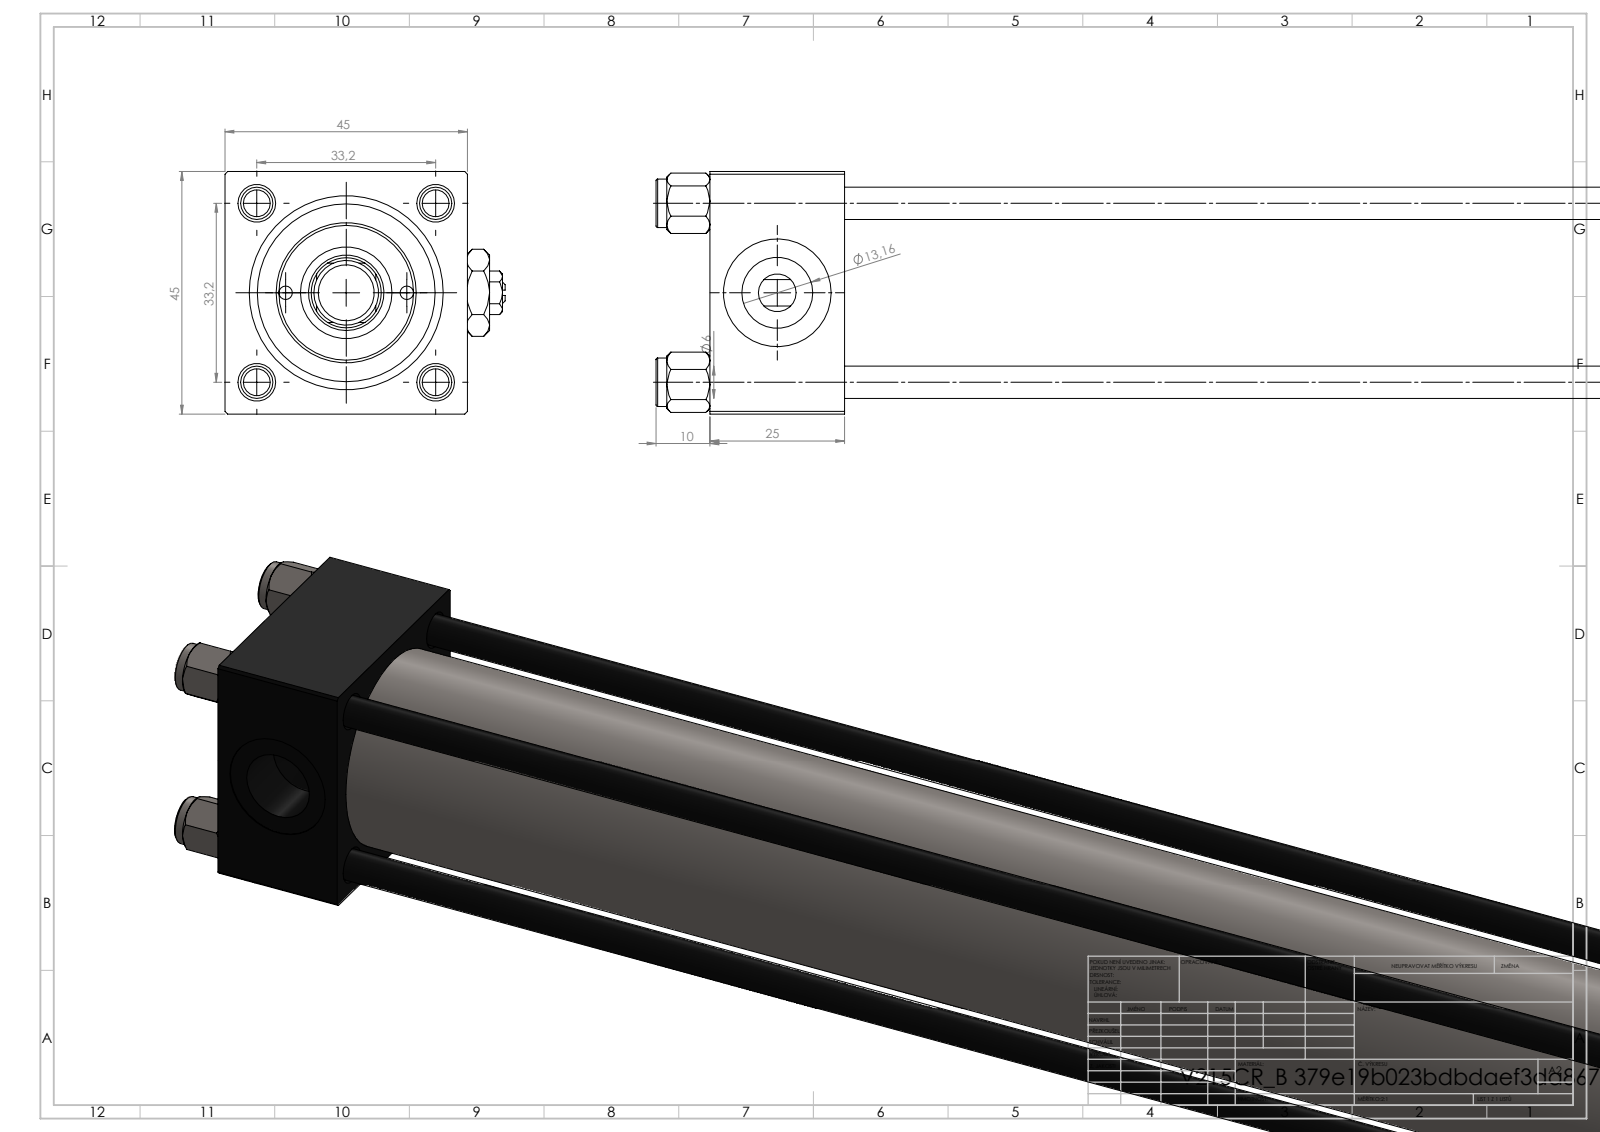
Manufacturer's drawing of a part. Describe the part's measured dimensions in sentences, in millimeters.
The part is named "V215CR_B-1; Zatka_pro_OIL_PORT; V215_VC_A; V215CR_B_TYCINKA (+3 more)". Its 3-D file was written by "SolidWorks 2019 (CONFIG_CONTROL_DESIGN)". It is 13 solids with 1228 faces: 460 planar, 92 cylindrical and 676 other. Overall it measures 404 by 52 by 45 millimeters. Its volume is 336 408 cubic millimeters and its surface area 152 741 square millimeters. Round holes: 4 of diameter 6, 2 of diameter 2.5, 2 of diameter 7, 2 of diameter 13.16, 2 of diameter 20, 1 of diameter 6.5, 1 of diameter 14, 1 of diameter 17, 1 of diameter 24, 1 of diameter 32, 1 of diameter 33. Round bosses or shafts: 4 of diameter 9, 1 of diameter 38, 1 of diameter 26, 1 of diameter 12, 1 of diameter 10. Partial cylindrical surfaces (rounded edges, fillets, slot ends): 1 of radius 6.5. The main face-to-face distances are 45, 25, 353, 328, 305, 280, 48, 324.3, 299.3, 19.3. The hole center spacings are 17.44, 23.48, 32.42, 33.2, 11.25, 46.95, 22.5, 305.5.
